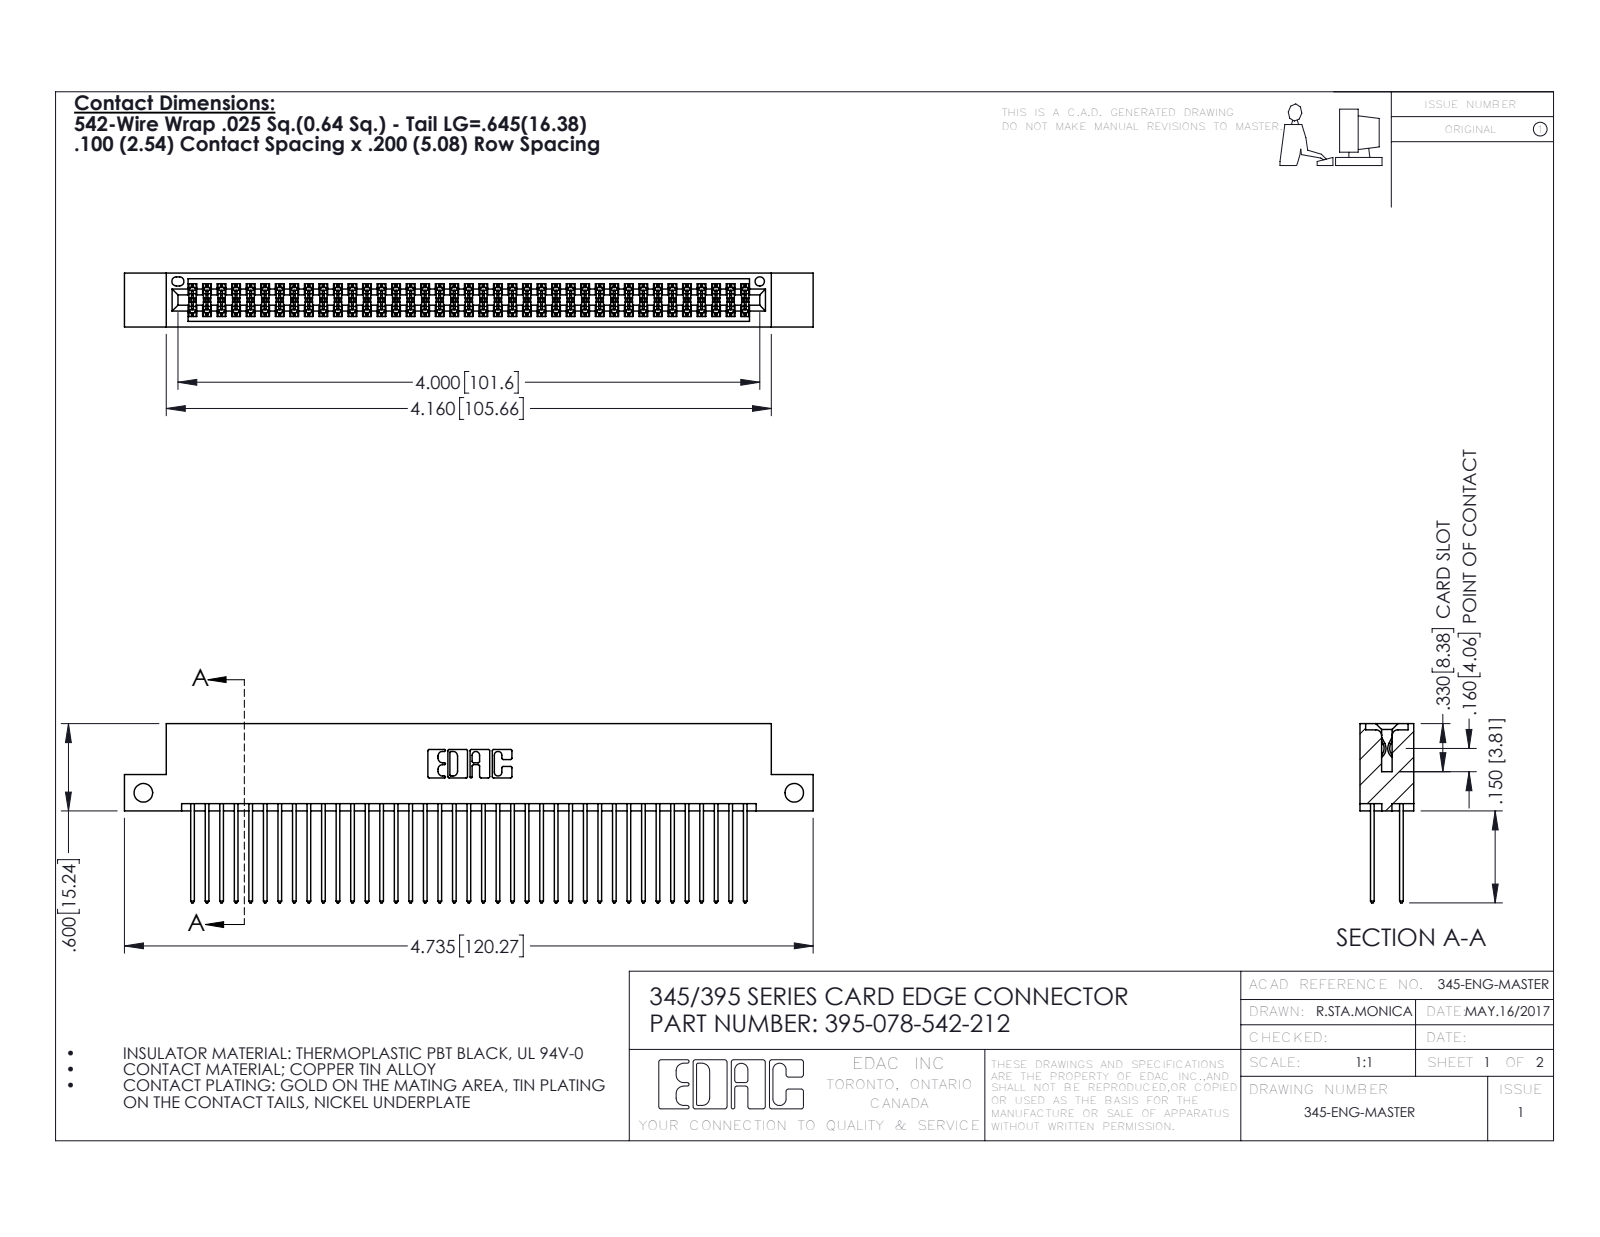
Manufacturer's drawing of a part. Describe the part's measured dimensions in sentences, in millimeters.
The part is named "345 Part_Flush Mounting Lugs - Side Mount; 395-078-542-212; 345-292-001_345-293-142". Its 3-D file was written by "SolidWorks 2016 (CONFIG_CONTROL_DESIGN)". It is 79 solids with 4026 faces: 2654 planar, 1372 cylindrical and 0 other. Overall it measures 120.3 by 31.3 by 9.4 millimeters. Its volume is 11 900 cubic millimeters and its surface area 19 140 square millimeters. Round holes: 2 of diameter 3.3, 1 of diameter 1.6. Partial cylindrical surfaces (rounded edges, fillets, slot ends): 117 of radius 0.2, 78 of radius 0.3, 22 of radius 0.3, 6 of radius 0.2, 6 of radius 0.8, 3 of radius 0.7, 2 of radius 0.4, 2 of radius 0.5. The main face-to-face distances are 7.6, 1.8, 5.1, 2.5, 6.9, 0.6, 5.7, 9.4, 4.4, 3.8. The hole center spacings are 113.7.
